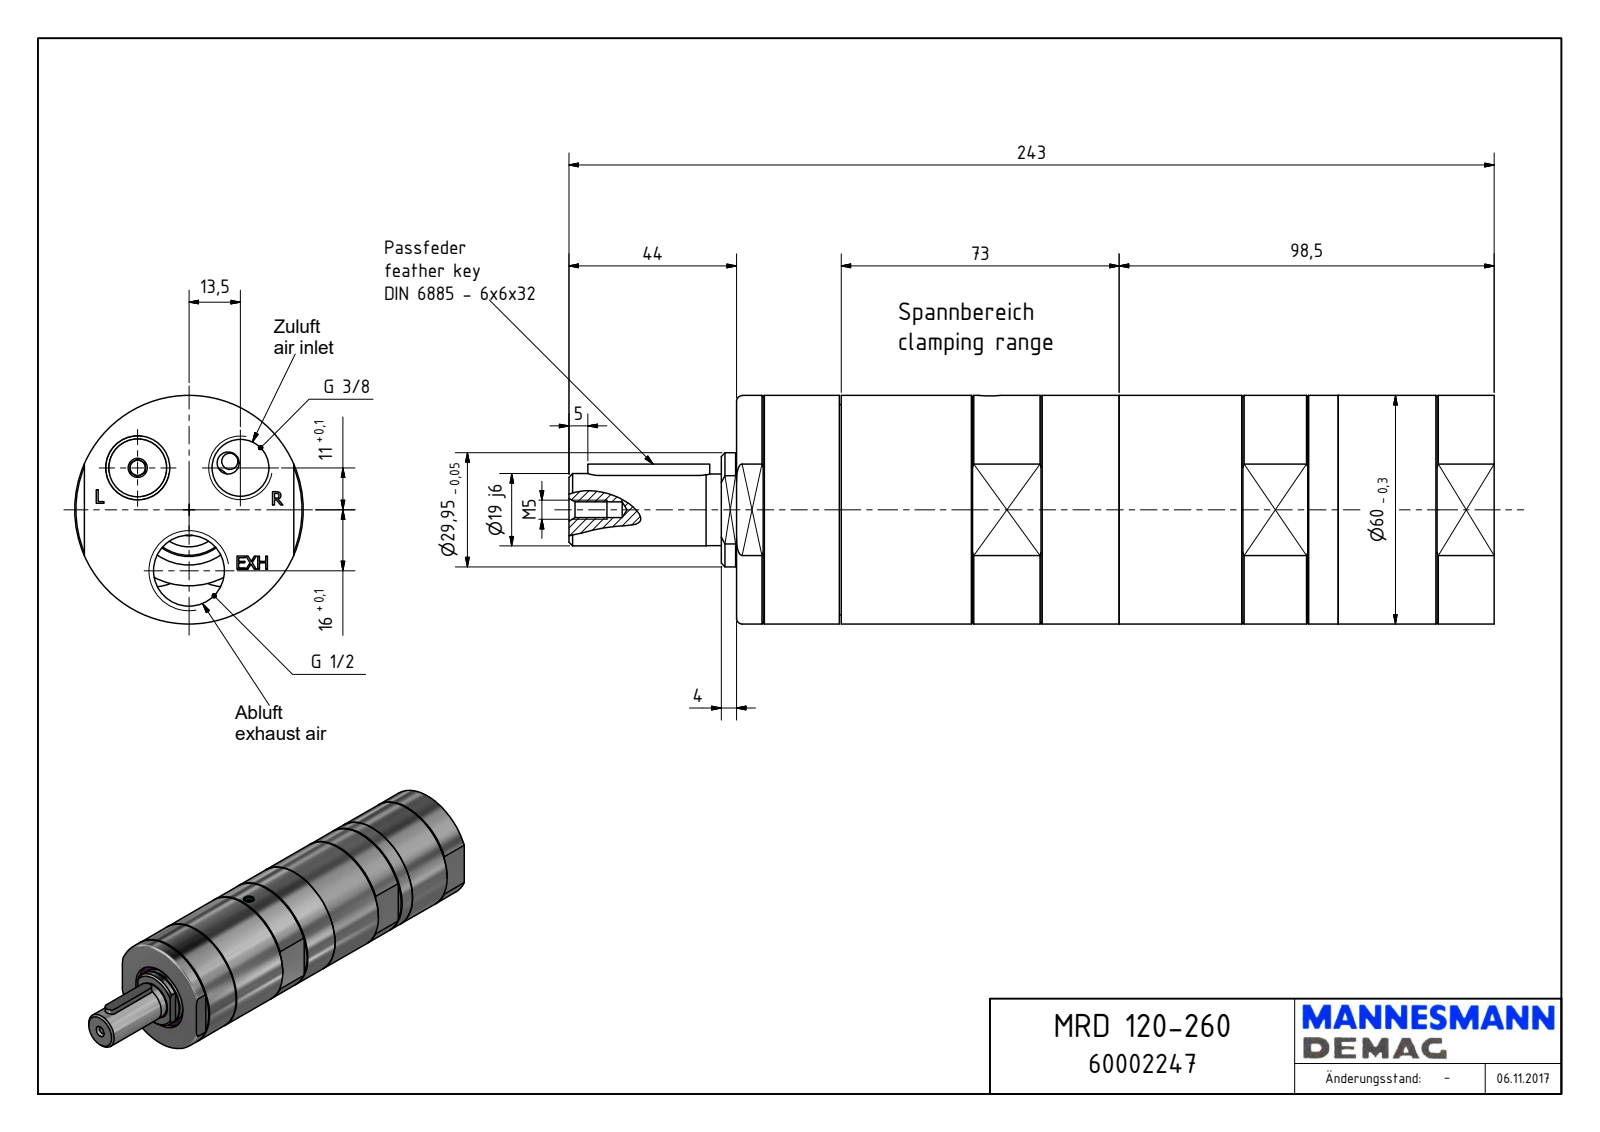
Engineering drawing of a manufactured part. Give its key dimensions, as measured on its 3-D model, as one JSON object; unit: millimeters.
{"part_name": "MRD 120-260_60002247", "step_written_by": "Autodesk Inventor 2018 (AUTOMOTIVE_DESIGN)", "units": "millimeters", "bodies": {"solids": 1, "faces": 219, "planar": 123, "cylindrical": 47, "other": 49}, "overall_size": [243, 60, 60], "volume_mm3": 559936, "surface_area_mm2": 53633, "round_holes": [[4, 2], [14.95, 2], [1.55, 1], [4.13, 1], [5.5, 1], [18.63, 1], [35, 1], [53.38, 1], [55.38, 1]], "round_bosses_or_shafts": [[60, 1], [55.18, 1], [53.18, 1], [29.95, 1], [19, 1], [18.8, 1], [5, 1], [3.6, 1]], "partial_cylinders_radius": [[3, 2], [7.5, 2], [8.5, 1], [19.33, 1], [23.5, 1], [25.48, 1]], "face_to_face_distances": [199, 55, 183.37, 15.63, 2.63, 186, 13, 27.5, 155.87, 158.5], "hole_center_spacings": [17.41, 30.19, 16, 27]}
